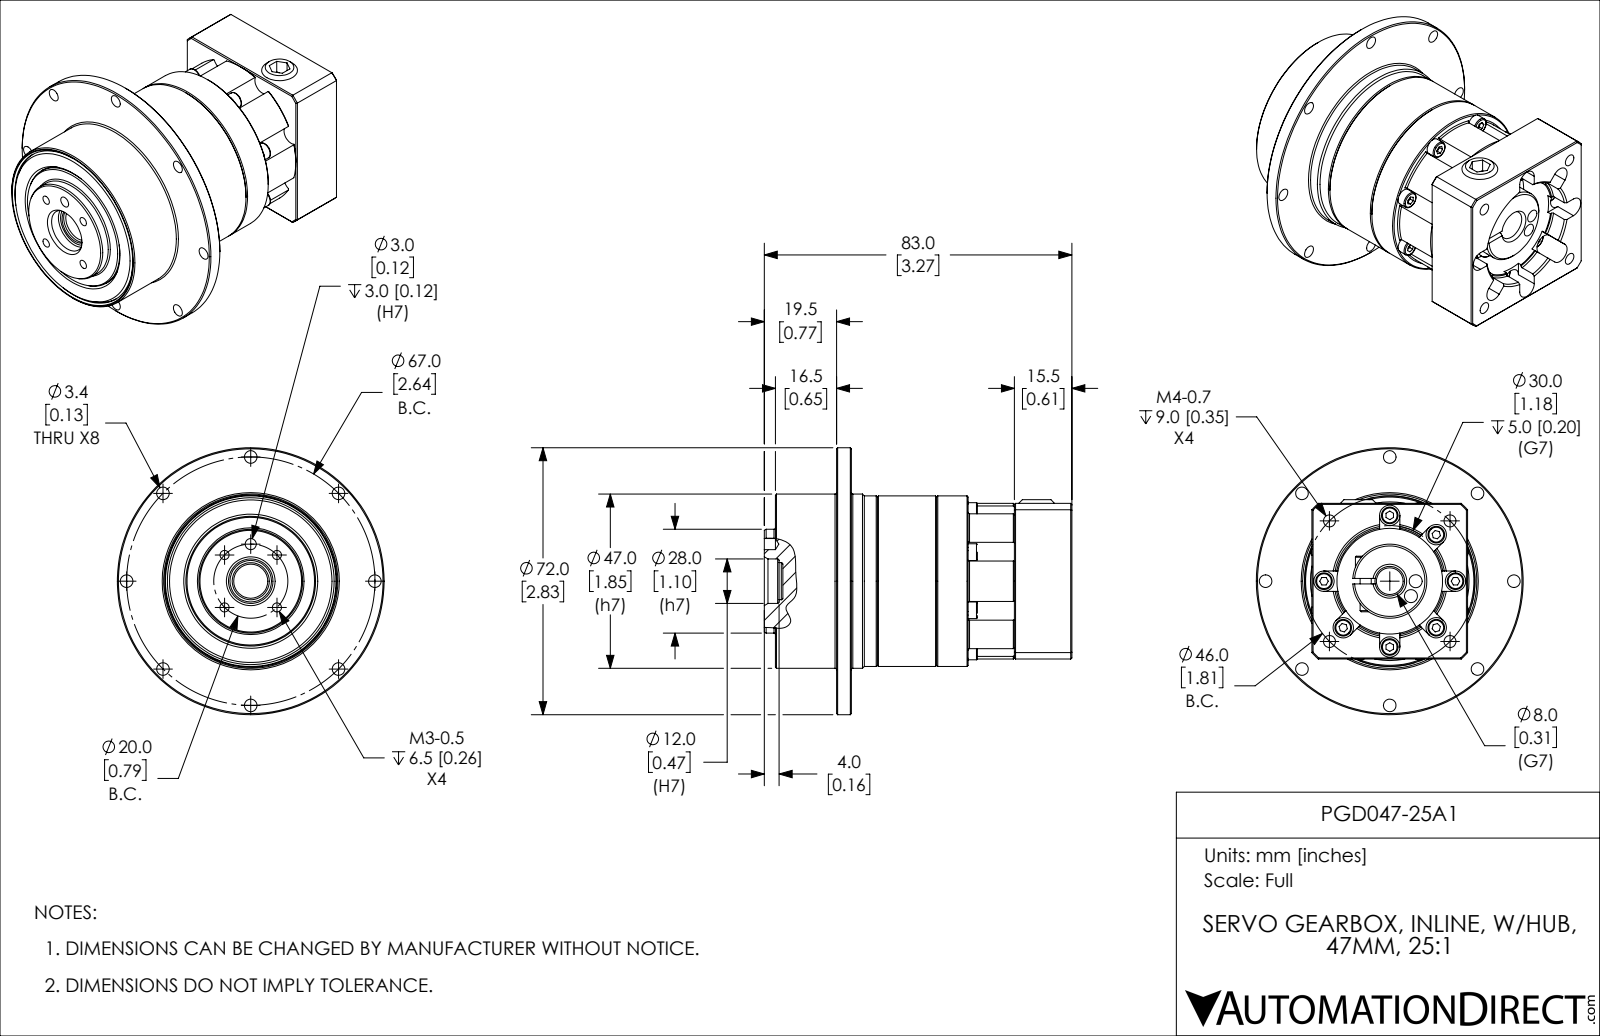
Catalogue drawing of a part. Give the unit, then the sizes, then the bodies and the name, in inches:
Units: inches
Overall size (bounding box): 3.268 × 2.835 × 2.835
Round holes (diameter × count): ⌀0.134 ×8, ⌀0.217 ×8, ⌀0.097 ×4, ⌀0.128 ×4, ⌀0.138 ×2, ⌀0.118 ×1, ⌀0.193 ×1, ⌀0.263 ×1, ⌀0.315 ×1, ⌀0.362 ×1, ⌀0.441 ×1, ⌀1.122 ×1
Round bosses / shafts (diameter × count): ⌀0.177 ×9, ⌀0.157 ×7, ⌀2.835 ×1, ⌀1.85 ×1, ⌀1.811 ×1, ⌀1.102 ×1, ⌀0.787 ×1, ⌀0.748 ×1
Partial cylindrical surfaces — rounded edges, fillets, slot ends (radius × count): R0.108 ×8, R0.128 ×1, R0.827 ×1, R1.122 ×1
Main face-to-face distances: 0.138, 0.433, 0.157, 0.276, 0.295, 0.945, 0.807, 1.654, 1.083, 0.65
Hole centre spacings: 0.961, 1.493, 1.879, 1.016, 1.077, 1.376, 0.504, 0.62
Volume: 8.182 in³ · Surface area: 53.7 in²
Bodies: 6 solids, 498 faces (278 planar, 147 cylindrical, 73 other)
Part name (STEP PRODUCT): PGD047-25A1
STEP written by: SolidWorks 2015 (AUTOMOTIVE_DESIGN)
